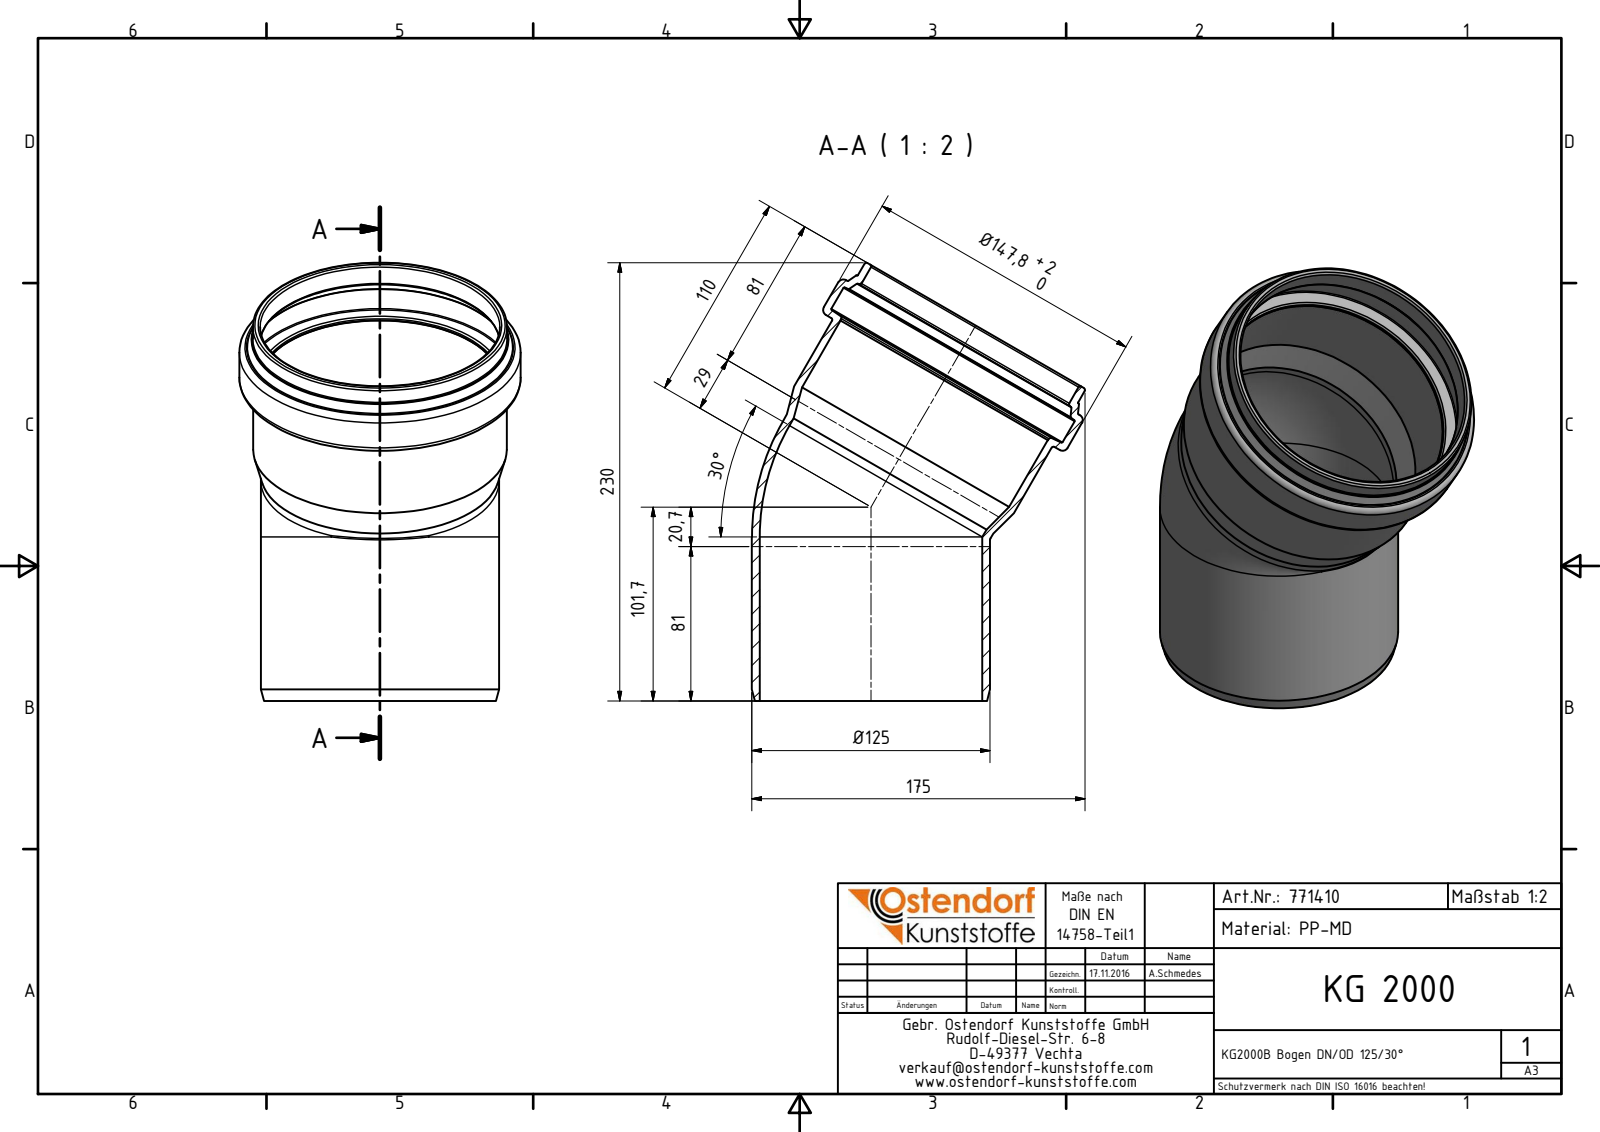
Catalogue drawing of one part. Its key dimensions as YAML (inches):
part_name: "771410 KG2000B Bogen DN_OD 125_30°"
step_written_by: "Autodesk Inventor 2016 (AUTOMOTIVE_DESIGN)"
units: inches
bodies: {solids: 1, faces: 42, planar: 5, cylindrical: 11, other: 26}
overall_size: [9.055, 6.89, 5.819]
volume: 20.93
surface_area: 275.4
round_holes:
  - {diameter: 4.602, count: 2}
  - {diameter: 4.945, count: 1}
  - {diameter: 4.957, count: 1}
  - {diameter: 5.52, count: 1}
round_bosses_or_shafts:
  - {diameter: 4.925, count: 2}
  - {diameter: 5.819, count: 1}
  - {diameter: 5.256, count: 1}
  - {diameter: 5.244, count: 1}
face_to_face_distances: [1.358, 0.831, 0.528, 0.05, 0.78, 1.308]
